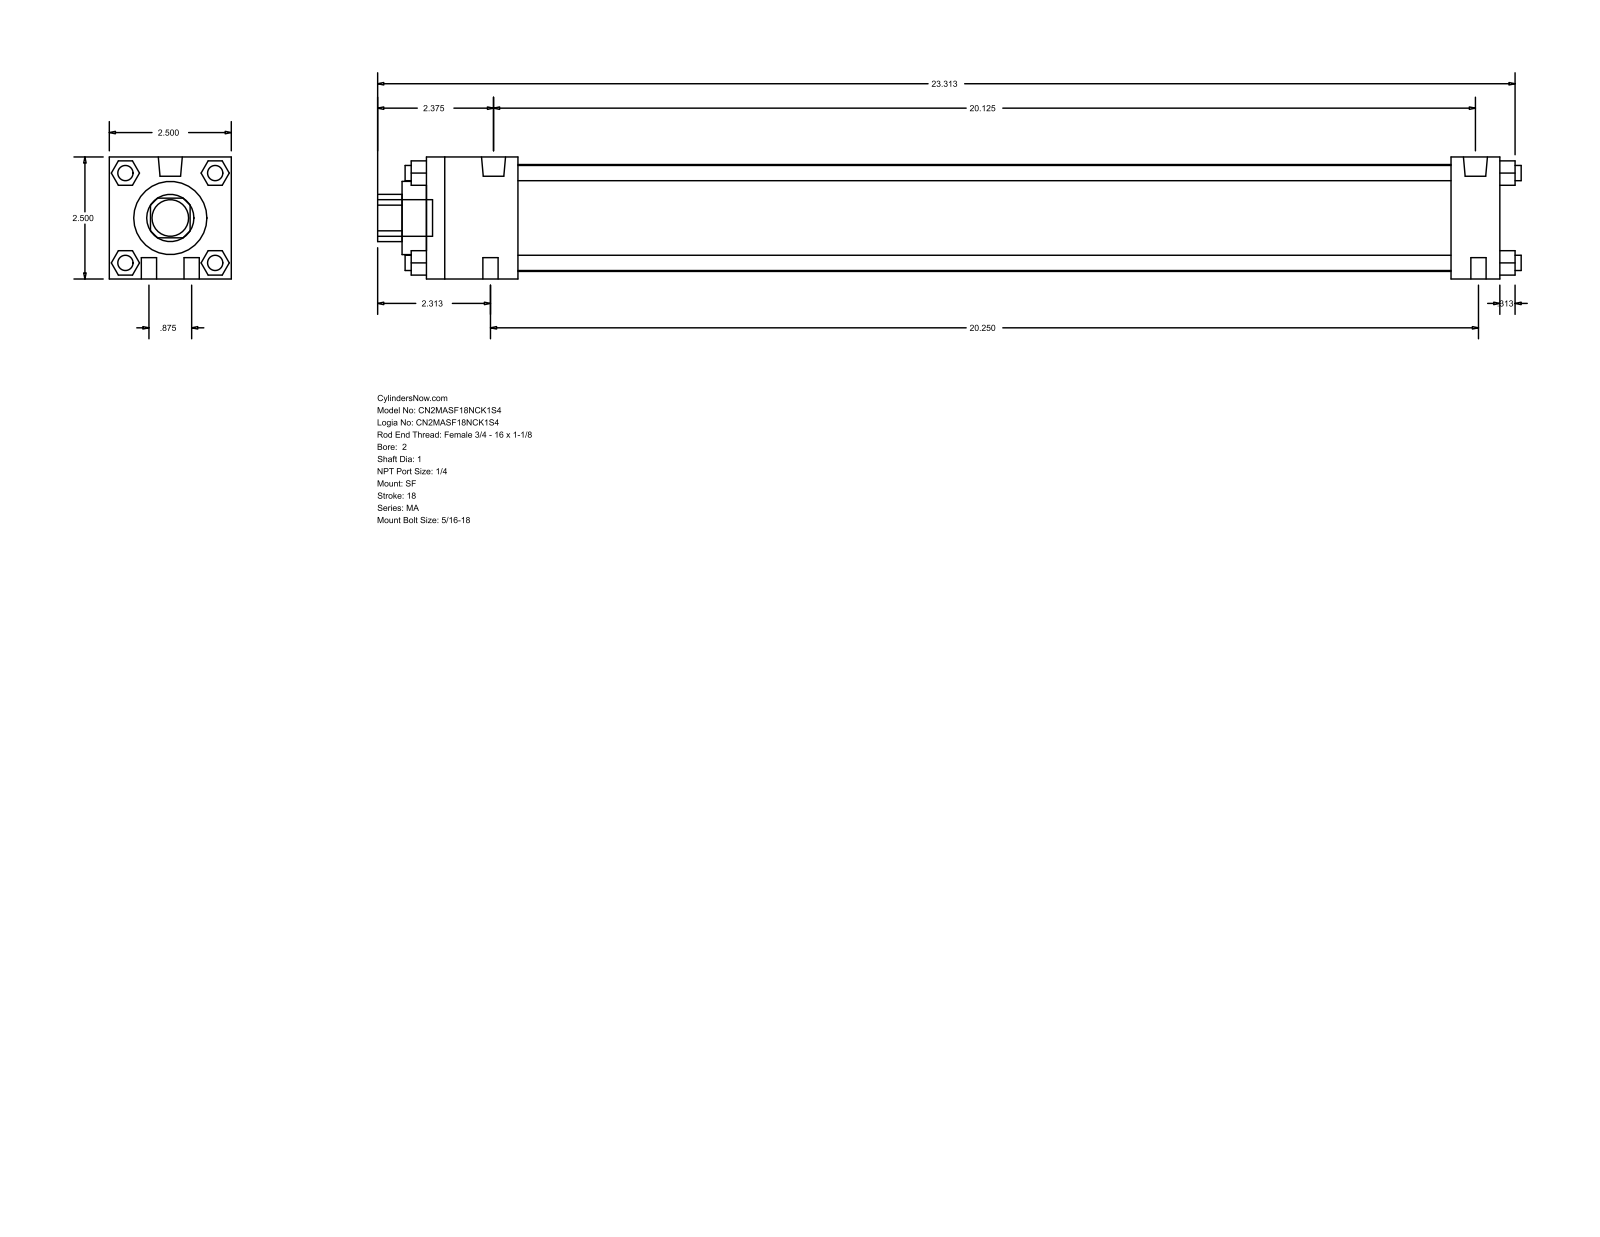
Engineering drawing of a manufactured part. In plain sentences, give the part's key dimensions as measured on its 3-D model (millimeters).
The part is named "MA_SF__0200_1". Its 3-D file was written by "GSSL Pune (CONFIG_CONTROL_DESIGN)". It is 0 solids with 124 faces: 94 planar, 30 cylindrical and 0 other. Overall it measures 595.31 by 63.5 by 63.5 millimeters. Round holes: 1 of diameter 25.4, 1 of diameter 38.1, 1 of diameter 55.63. Round bosses or shafts: 10 of diameter 7.94, 2 of diameter 12.49, 1 of diameter 19.05. Partial cylindrical surfaces (rounded edges, fillets, slot ends): 1 of radius 12.29. The main face-to-face distances are 63.5, 558.8, 12.7, 25.4, 533.4, 47.63, 485.77, 511.17, 23.37, 40.47.
